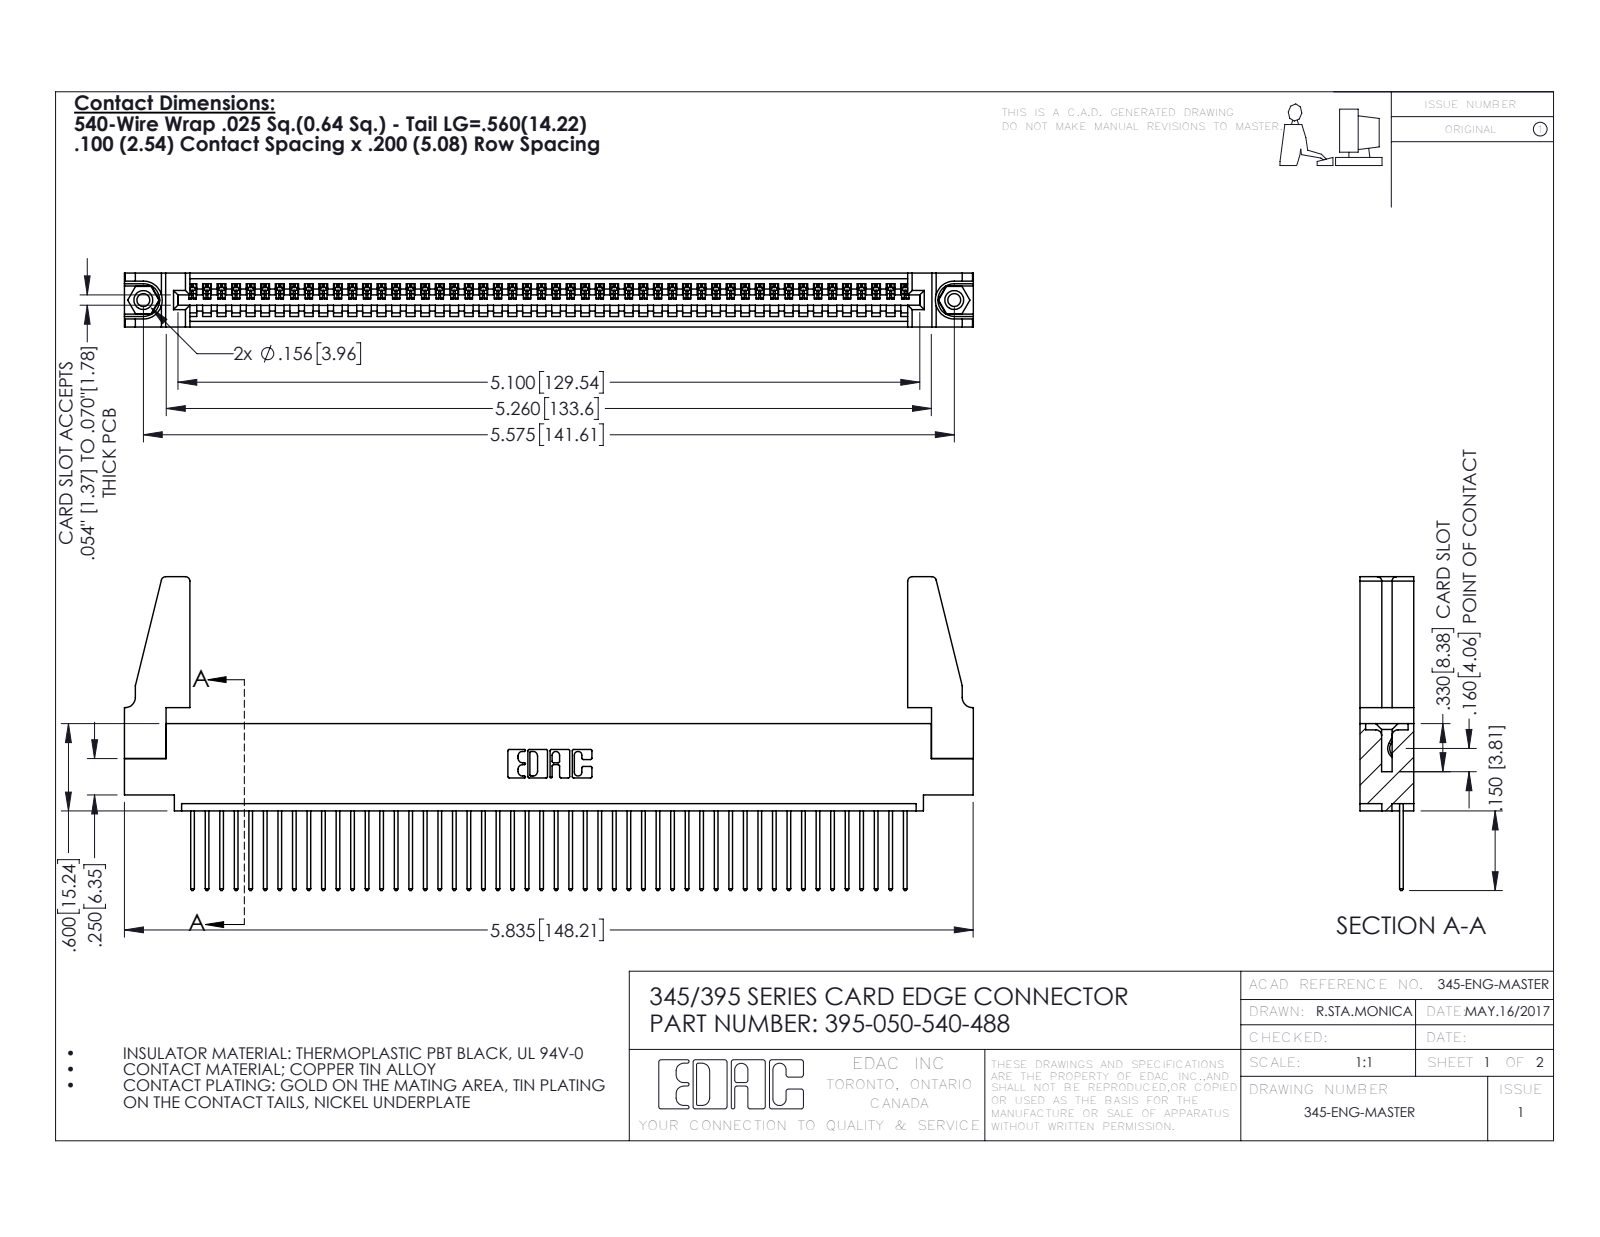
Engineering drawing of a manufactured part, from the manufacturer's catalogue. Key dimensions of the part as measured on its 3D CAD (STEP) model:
Part name (STEP PRODUCT): 345-220-078_345-220-088; 345-292-001_345-293-140; 345-250-001_345-250-001-102; 345 Part_0.110 Offset - 0.156 Dia-TH (+1 more)
STEP written by: SolidWorks 2016 (CONFIG_CONTROL_DESIGN)
Units: inches
Bodies: 55 solids, 3154 faces (2156 planar, 982 cylindrical, 16 other)
Overall size (bounding box): 5.836 × 2.157 × 0.37
Volume: 1.061 in³ · Surface area: 35.03 in²
Round holes (diameter × count): ⌀0.089 ×2, ⌀0.125 ×2, ⌀0.156 ×2, ⌀0.064 ×1
Round bosses / shafts (diameter × count): ⌀0.155 ×2
Partial cylindrical surfaces — rounded edges, fillets, slot ends (radius × count): R0.006 ×100, R0.01 ×100, R0.01 ×22, R0.03 ×8, R0.007 ×6, R0.031 ×6, R0.026 ×3, R0.031 ×2
Main face-to-face distances: 0.072, 0.298, 0.37, 0.098, 0.272, 0.025, 0.2, 0.225, 0.149, 0.072
Hole centre spacings: 0.27, 5.339, 5.575
